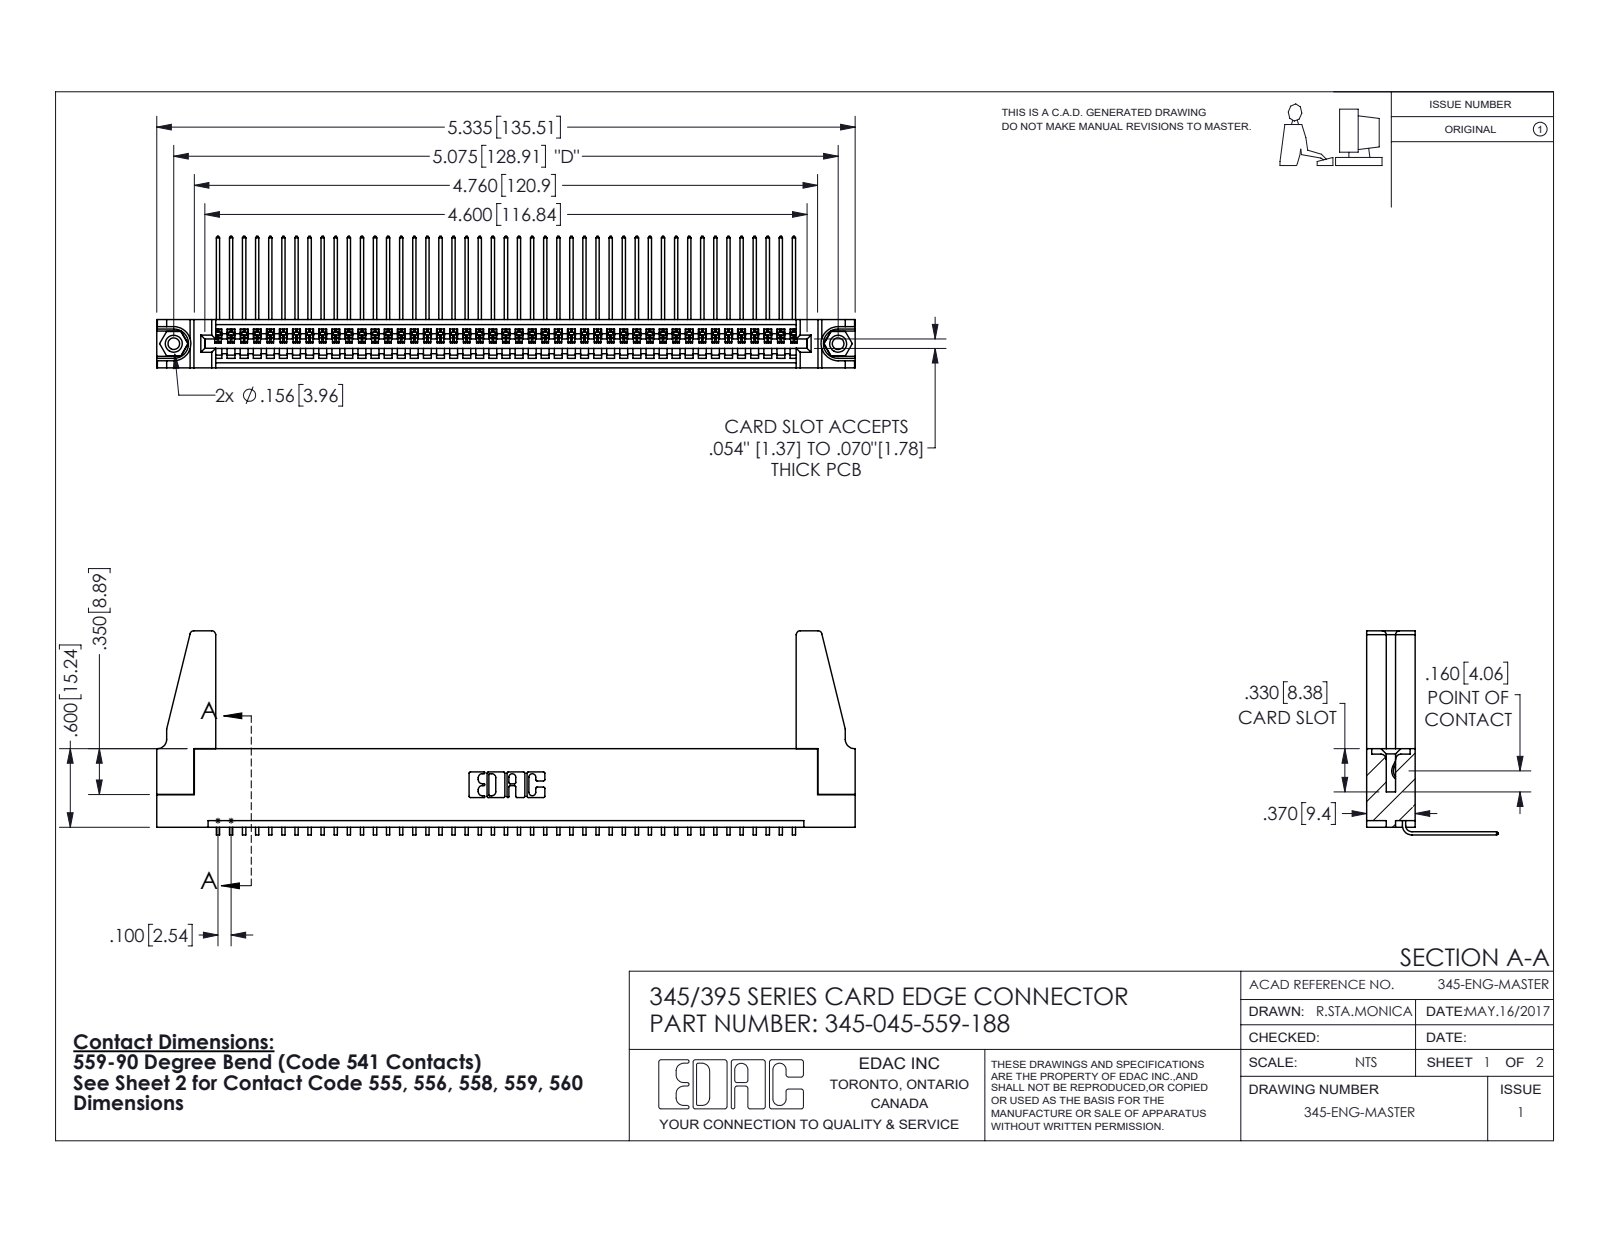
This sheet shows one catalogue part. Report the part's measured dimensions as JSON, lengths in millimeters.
{"part_name": "345-220-078_345-220-088; 345-045-559-188; 345-292-001_558 559 Tail - 1; 345 Part_Flush Mounting Lugs - 0.156 Dia-TH (+1 more)", "step_written_by": "SolidWorks 2016 (CONFIG_CONTROL_DESIGN)", "units": "millimeters", "bodies": {"solids": 50, "faces": 2950, "planar": 2042, "cylindrical": 892, "other": 16}, "overall_size": [135.5, 39.6, 25.5], "volume_mm3": 16300, "surface_area_mm2": 21390, "round_holes": [[2.3, 2], [3.2, 2], [4, 2], [1.6, 1]], "round_bosses_or_shafts": [[3.9, 2]], "partial_cylinders_radius": [[0.2, 90], [0.3, 22], [0.8, 8], [0.2, 6], [0.8, 6], [0.7, 3], [0.8, 2], [1, 2]], "face_to_face_distances": [1.8, 7.6, 9.4, 5.1, 2.5, 6.9, 0.6, 5.7, 3.8, 1.8], "hole_center_spacings": [6.9, 122.9, 128.9]}
